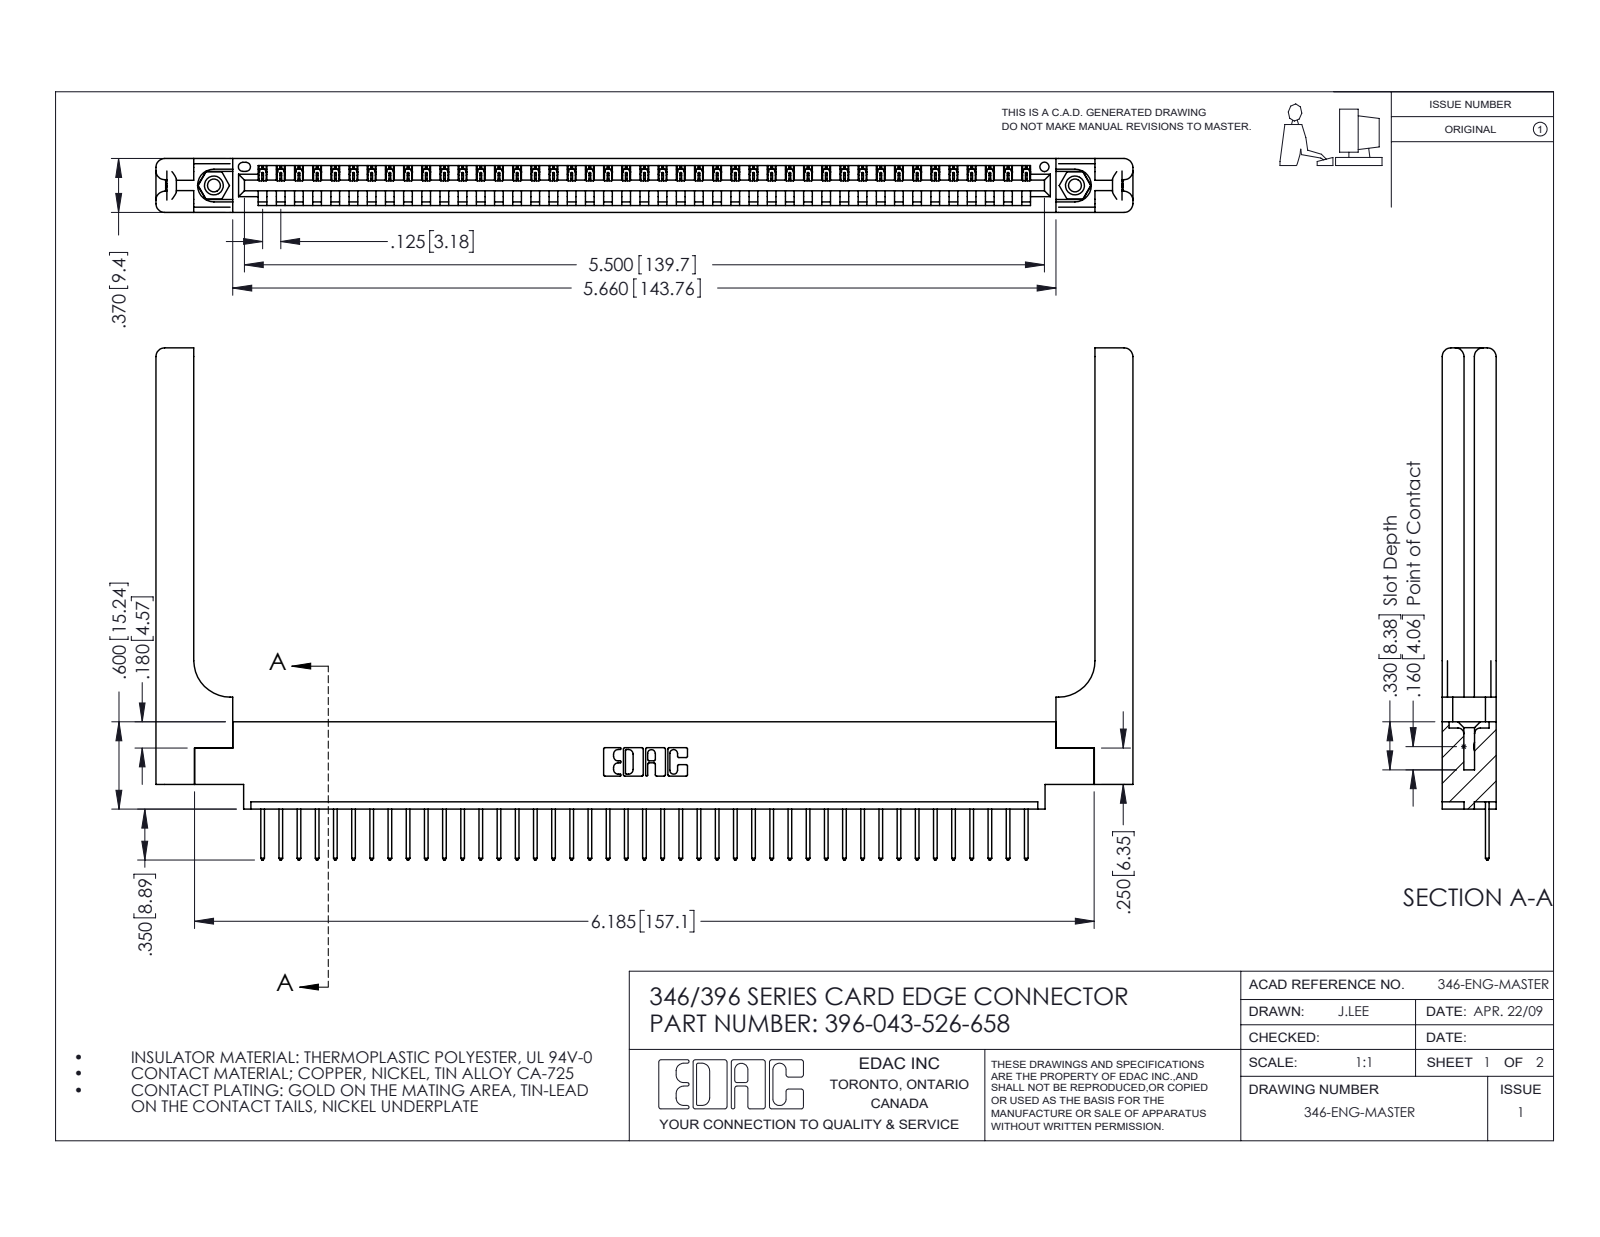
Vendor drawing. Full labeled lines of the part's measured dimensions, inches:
Part name (STEP PRODUCT): 346 Part_0.170 Offset - 0.156 Dia-TH; 345-292-001_345-293-126; 345-250-001_345-250-001-102; 346-220-058_345-220-058 (+1 more)
STEP written by: SolidWorks 2016 (CONFIG_CONTROL_DESIGN)
Units: inches
Bodies: 48 solids, 2876 faces (1948 planar, 868 cylindrical, 60 other)
Overall size (bounding box): 6.716 × 3.52 × 0.37
Volume: 1.444 in³ · Surface area: 39.49 in²
Round holes (diameter × count): ⌀0.089 ×2, ⌀0.125 ×2, ⌀0.156 ×2, ⌀0.064 ×1
Round bosses / shafts (diameter × count): ⌀0.155 ×2
Partial cylindrical surfaces — rounded edges, fillets, slot ends (radius × count): R0.006 ×86, R0.01 ×86, R0.01 ×22, R0.06 ×16, R0.007 ×6, R0.031 ×6, R0.026 ×3, R0.03 ×2
Main face-to-face distances: 0.37, 0.048, 0.322, 0.072, 0.148, 0.15, 0.25, 0.298, 0.025, 0.222
Hole centre spacings: 0.246, 5.711, 5.92
